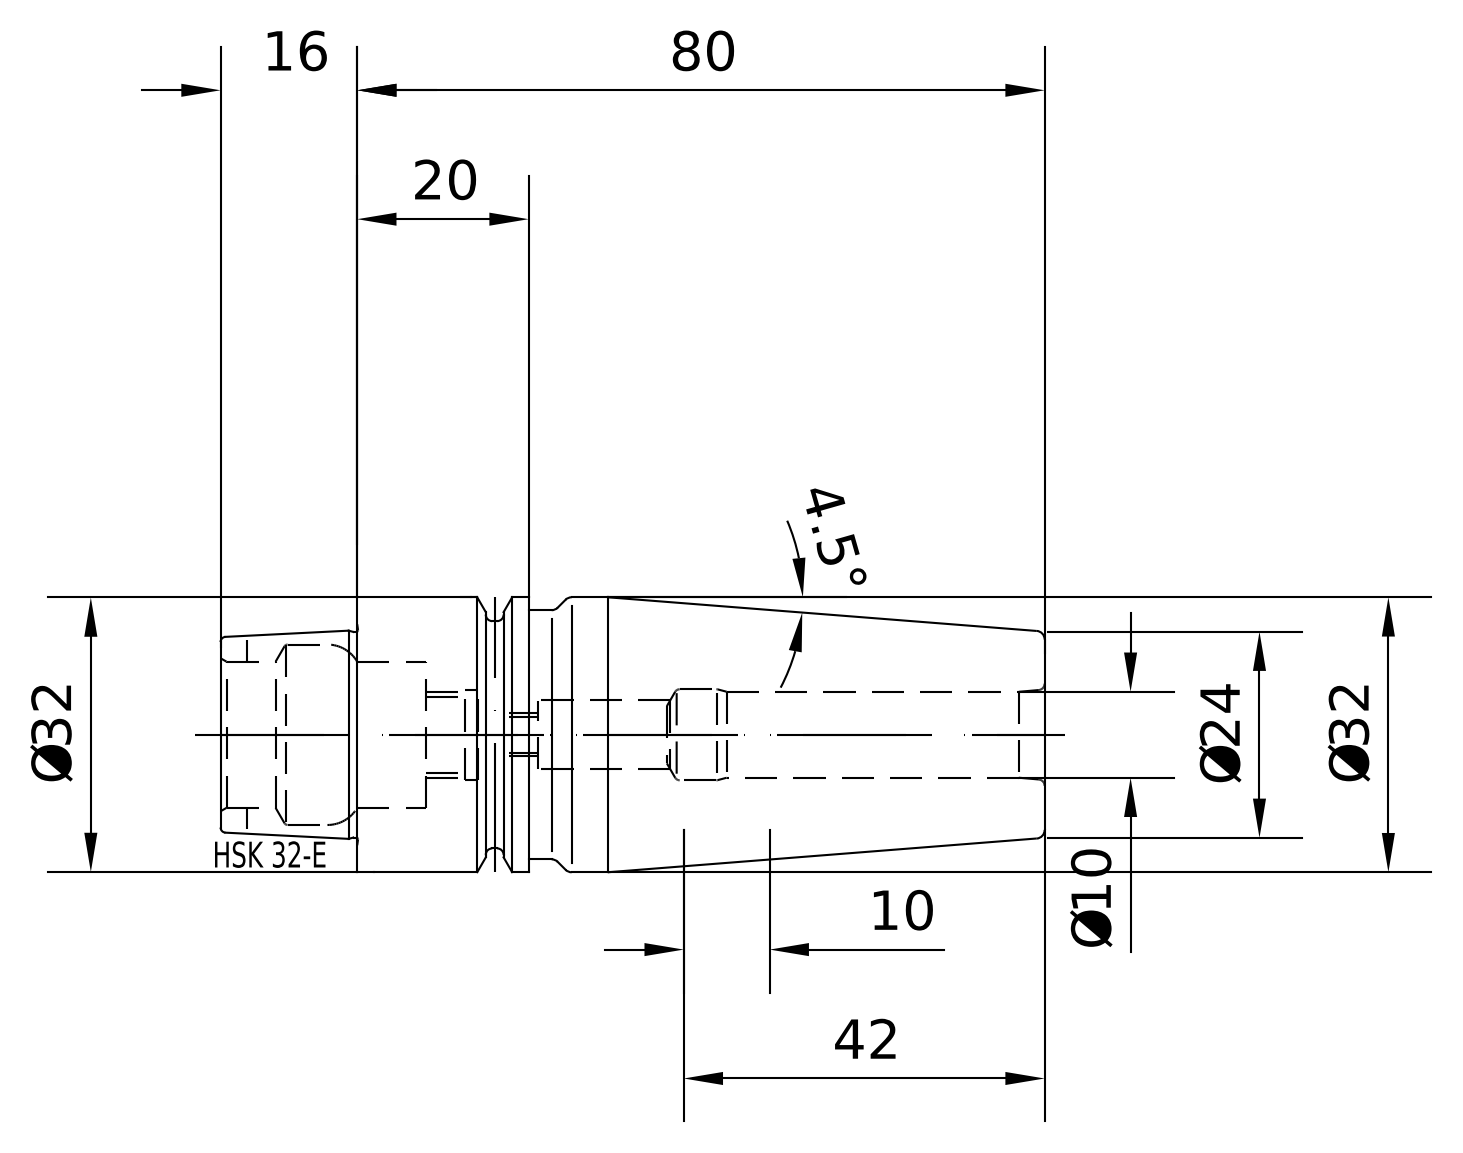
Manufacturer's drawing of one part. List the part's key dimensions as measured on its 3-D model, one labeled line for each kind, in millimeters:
Part name (STEP PRODUCT): E32-140-10
STEP written by: PRO/ENGINEER BY PARAMETRIC TECHNOLOGY CORPORATION, 2010430 (CONFIG_CONTROL_DESIGN)
Units: millimetres
Bodies: 1 solid, 84 faces (10 planar, 24 cylindrical, 50 other)
Overall size (bounding box): 95.9 × 32 × 32
Volume: 45 733 mm³ · Surface area: 13 217 mm²
Round holes (diameter × count): ⌀8.5 ×1, ⌀10 ×1, ⌀10.22 ×1, ⌀10.5 ×1, ⌀17.04 ×1, ⌀21.07 ×1
Round bosses / shafts (diameter × count): ⌀32 ×1, ⌀26.45 ×1, ⌀24.03 ×1, ⌀24 ×1
Main face-to-face distances: 60.05, 19.95, 80, 6, 35.45, 15.5, 44.55, 7.95, 12, 27.5
